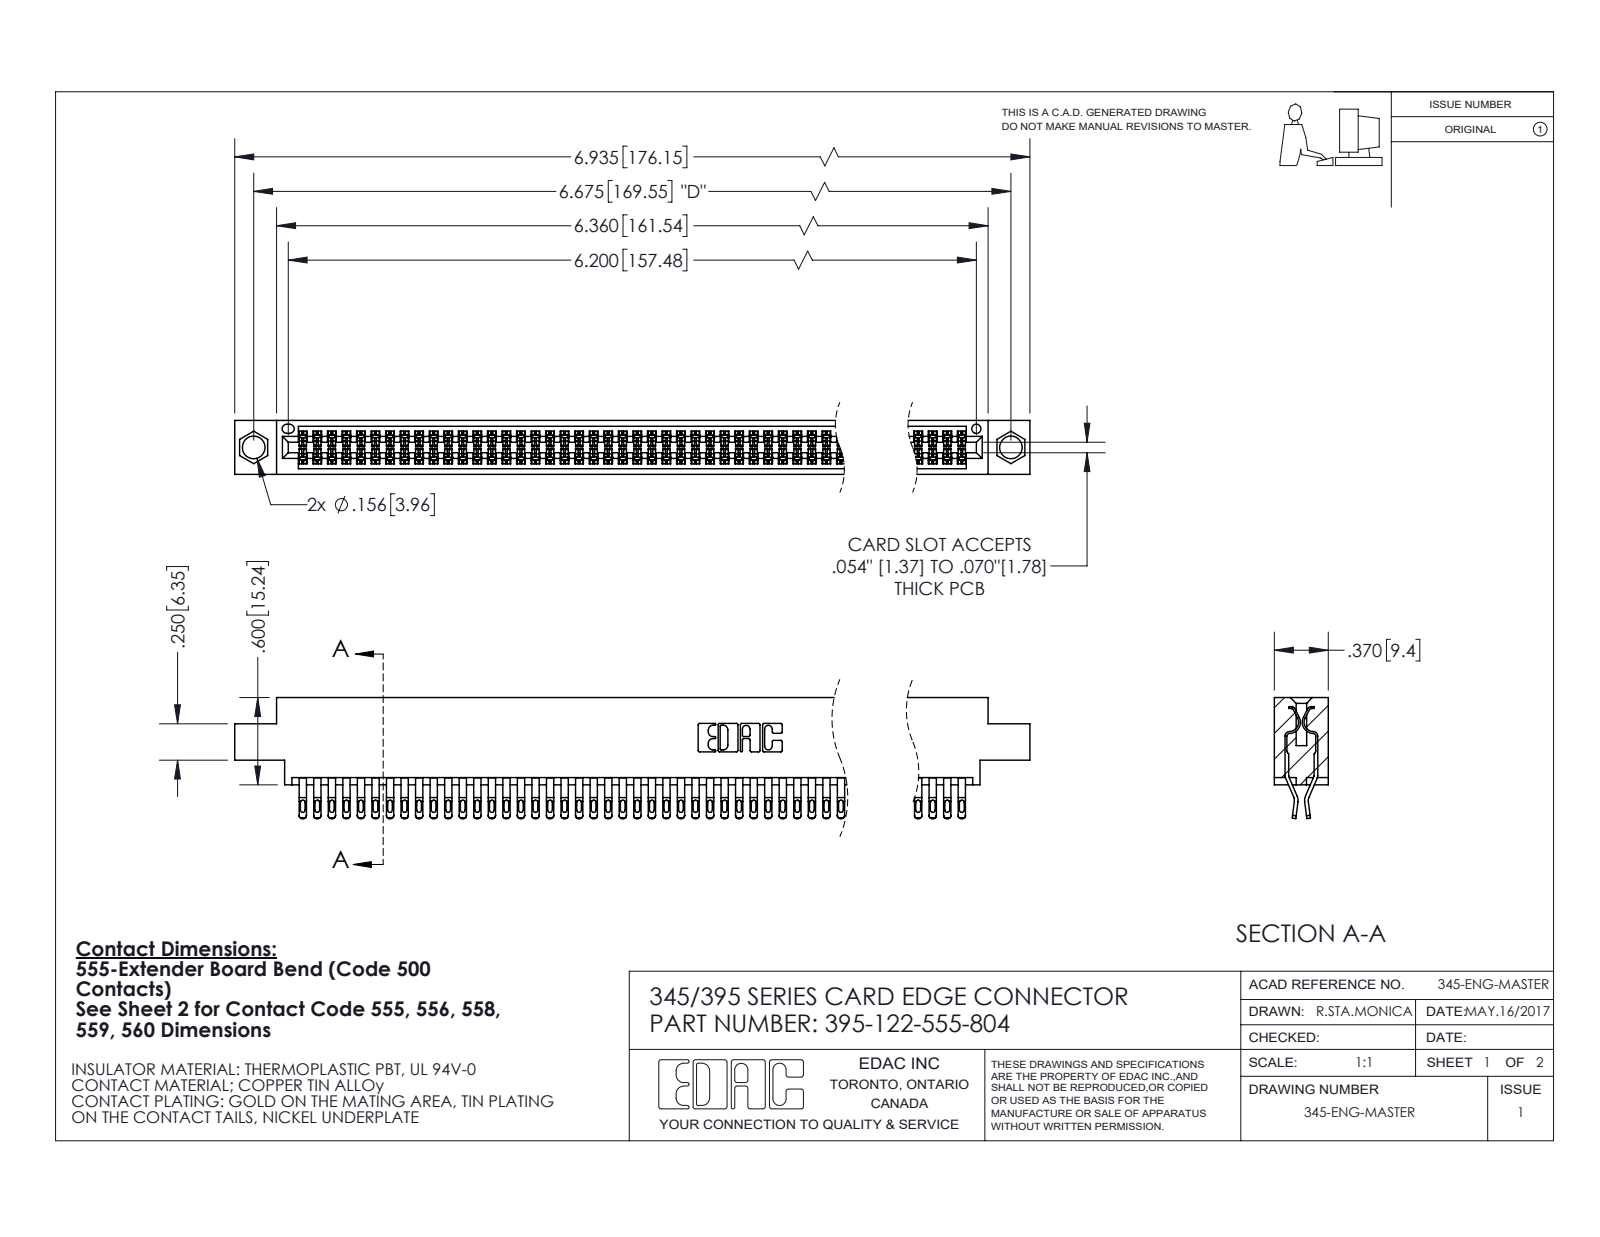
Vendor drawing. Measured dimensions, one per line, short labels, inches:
name: 345-292-001_555 Tail; 345 Part_0.170 Offset - 0.156 Dia-TI; 395-122-555-804
written by: SolidWorks 2020 (CONFIG_CONTROL_DESIGN)
unit: in
bodies: 123 solids, 6976 faces (3880 planar, 3096 cylindrical, 0 other)
size: 6.935 × 0.832 × 0.37
volume: 1.063 in³; area: 42.39 in²
holes: 2× ⌀0.156, 1× ⌀0.064
rounds: 305× R0.016, 244× R0.006, 244× R0.02, 22× R0.01, 6× R0.007, 6× R0.031, 3× R0.026, 2× R0.01
face distances: 0.072, 0.298, 0.025, 0.37, 0.2, 0.098, 0.272, 0.225, 0.175, 0.149
hole spacings: 0.27, 6.439, 6.675
